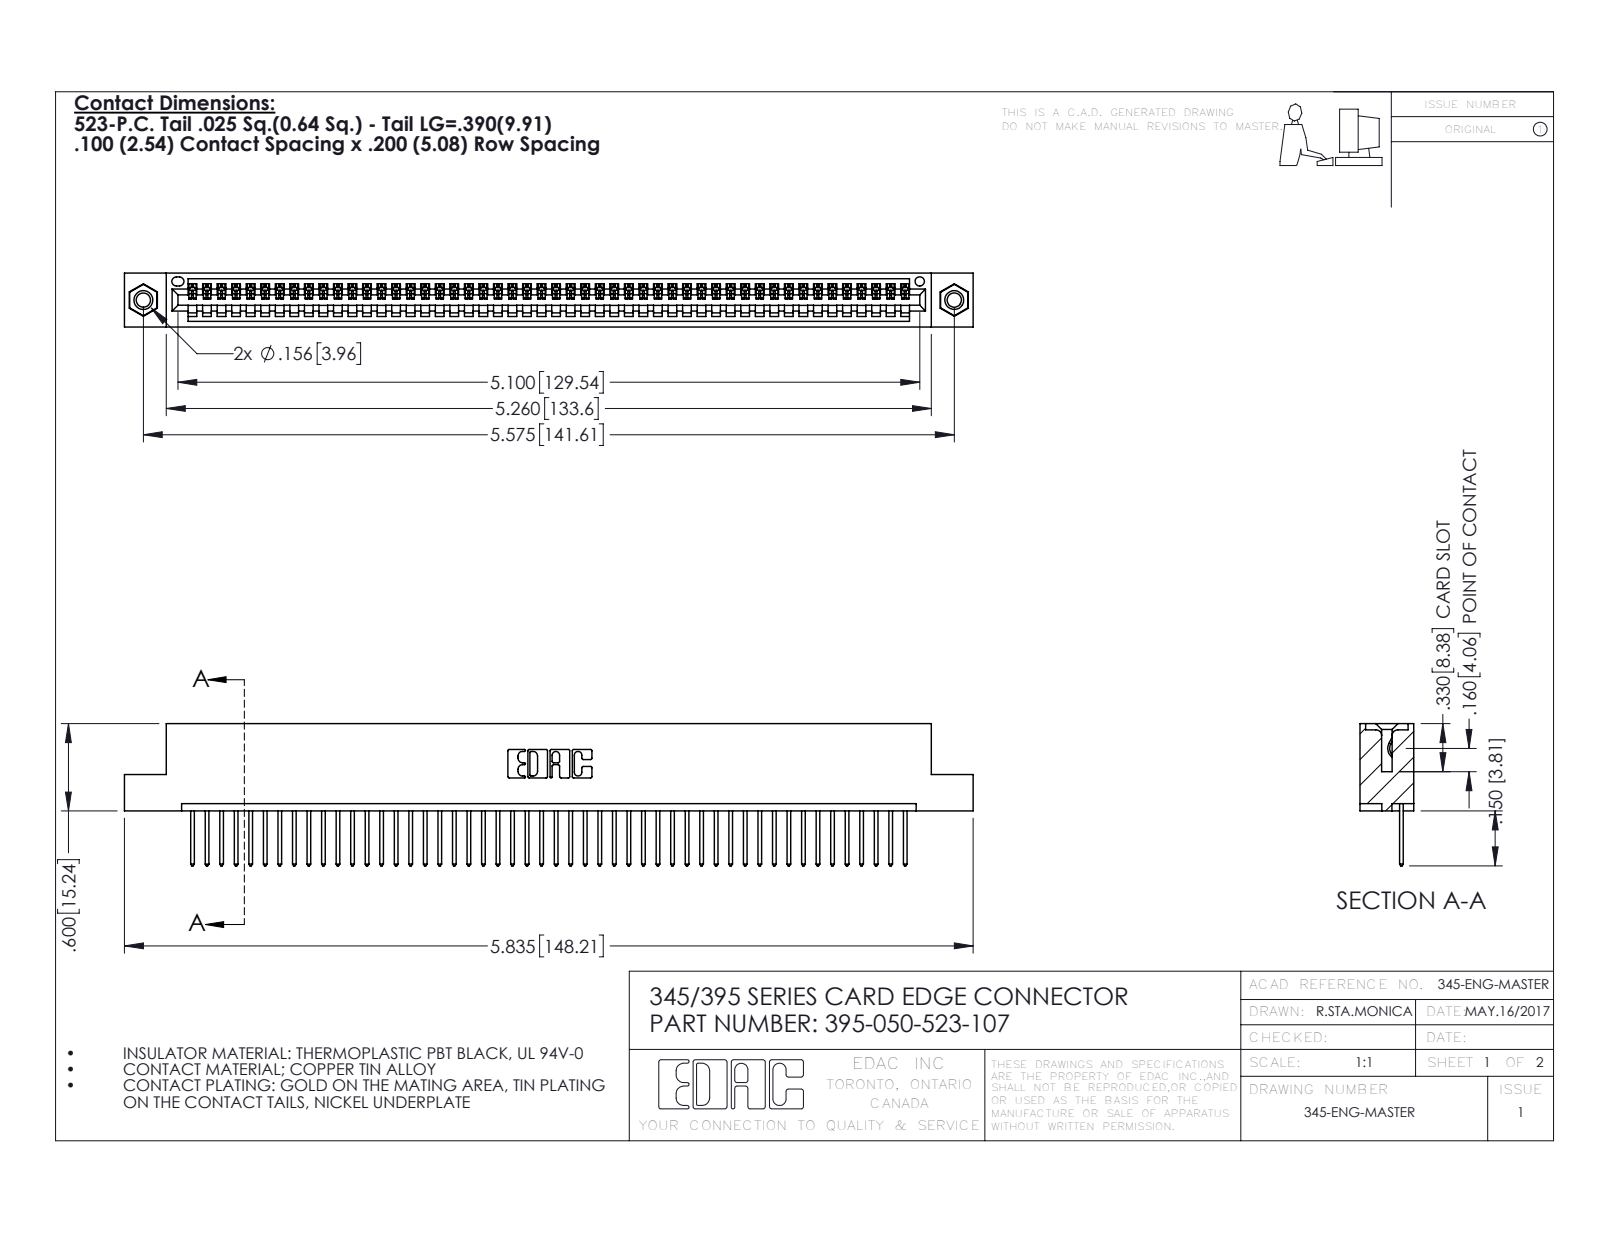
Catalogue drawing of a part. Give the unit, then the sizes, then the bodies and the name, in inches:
Units: inches
Overall size (bounding box): 5.835 × 0.977 × 0.37
Round holes (diameter × count): ⌀0.098 ×2, ⌀0.125 ×2, ⌀0.156 ×2, ⌀0.064 ×1
Round bosses / shafts (diameter × count): ⌀0.155 ×2
Partial cylindrical surfaces — rounded edges, fillets, slot ends (radius × count): R0.006 ×100, R0.01 ×100, R0.01 ×22, R0.007 ×6, R0.031 ×6, R0.026 ×3, R0.031 ×2, R0.04 ×2
Main face-to-face distances: 0.072, 0.298, 0.37, 0.2, 0.098, 0.272, 0.025, 0.225, 0.149, 0.072
Hole centre spacings: 0.27, 5.339, 5.575
Volume: 0.861 in³ · Surface area: 29.37 in²
Bodies: 53 solids, 3086 faces (2112 planar, 958 cylindrical, 16 other)
Part name (STEP PRODUCT): 395-050-523-107; 345 Part_Flush Mounting Lugs - 0.156 Dia-TI; 345-250-001_345-250-005-103; 345-292-001_345-293-123
STEP written by: SolidWorks 2016 (CONFIG_CONTROL_DESIGN)
